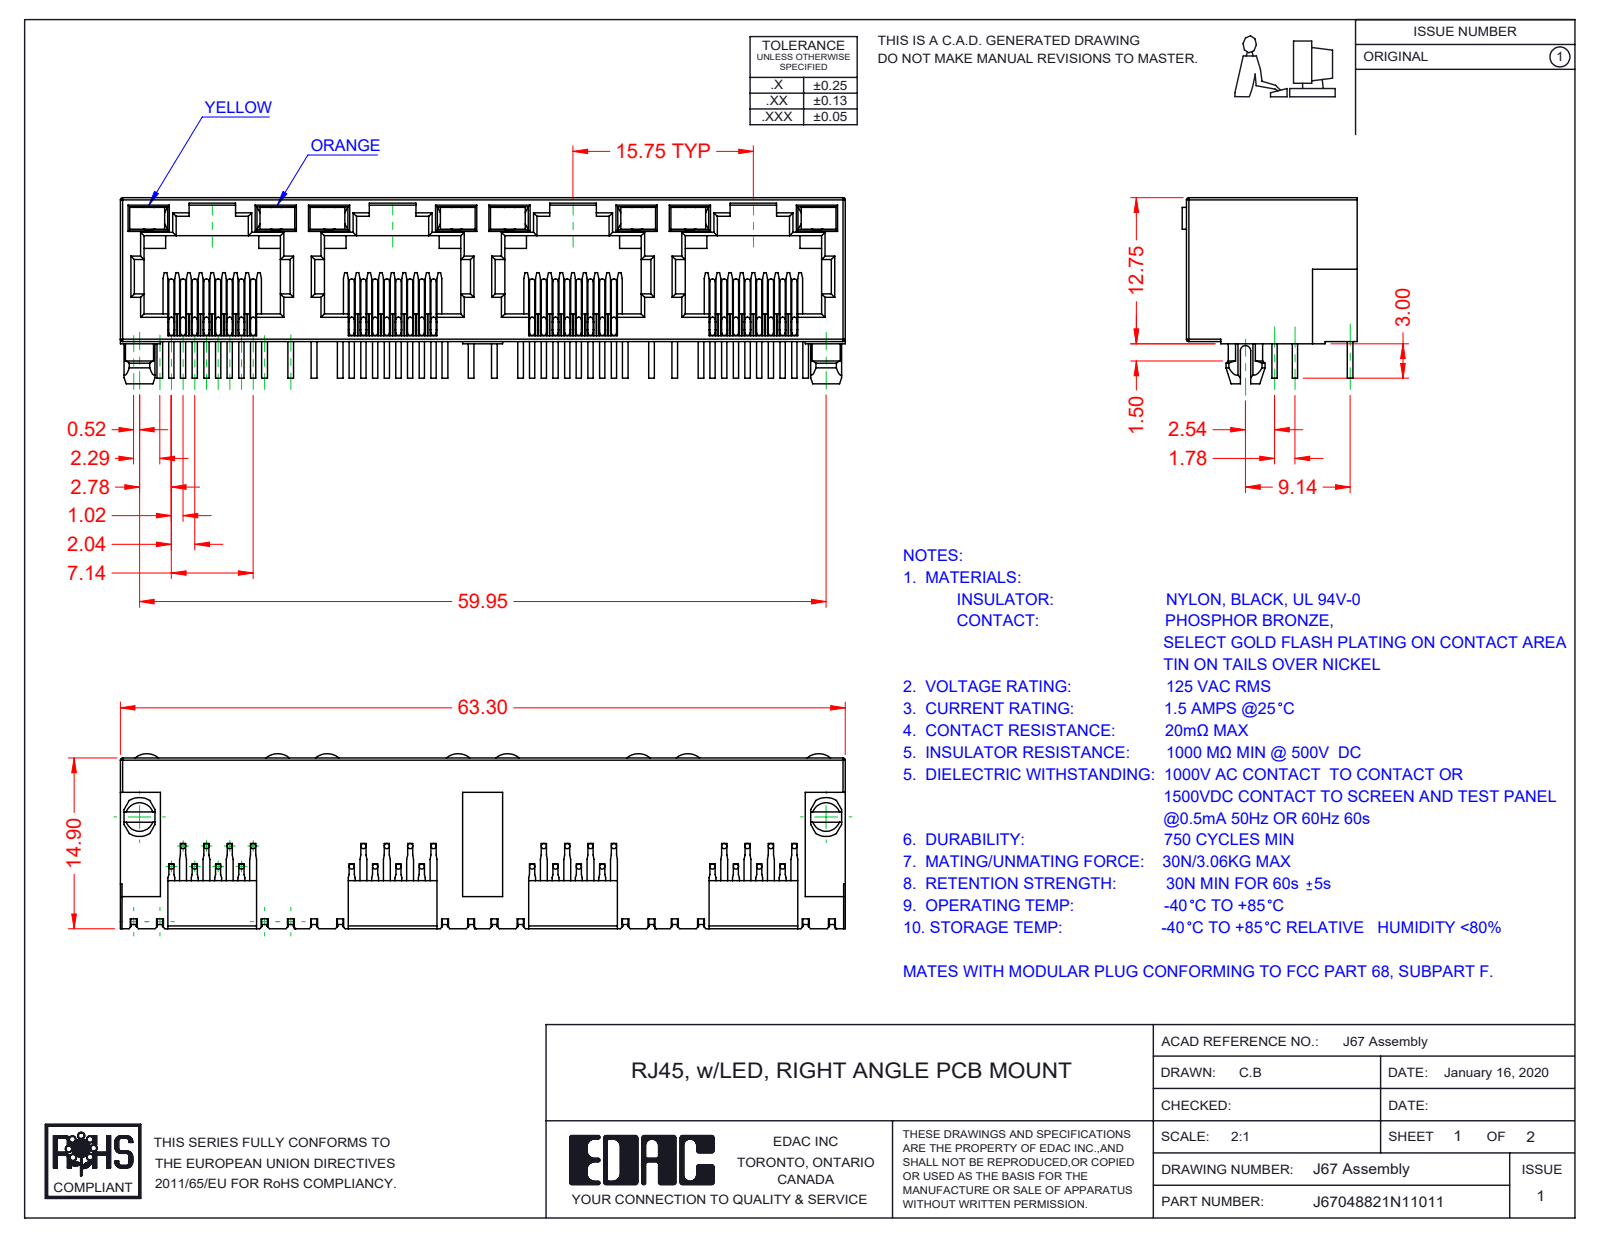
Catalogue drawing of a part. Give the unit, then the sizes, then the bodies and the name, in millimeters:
Units: millimetres
Overall size (bounding box): 63.3 × 16.25 × 15.28
Round bosses / shafts (diameter × count): ⌀0.46 ×96
Partial cylindrical surfaces — rounded edges, fillets, slot ends (radius × count): R0.2 ×66, R0.3 ×29, R0.45 ×9, R1.55 ×8, R1.5 ×2, R1.7 ×2, R0.35 ×1, R1 ×1
Main face-to-face distances: 0.5, 12.55, 1.89, 0.89, 10, 15.75, 1, 1.39, 11, 11.89
Volume: 5 159 mm³ · Surface area: 11 573 mm²
Bodies: 41 solids, 2465 faces (1781 planar, 476 cylindrical, 208 other)
Part name (STEP PRODUCT): J67048822N14011; 67 Insulator; 67 LED RH_4-Orange; 67 LED LH_1-Yellow (+1 more)
STEP written by: SolidWorks 2016 (CONFIG_CONTROL_DESIGN)
